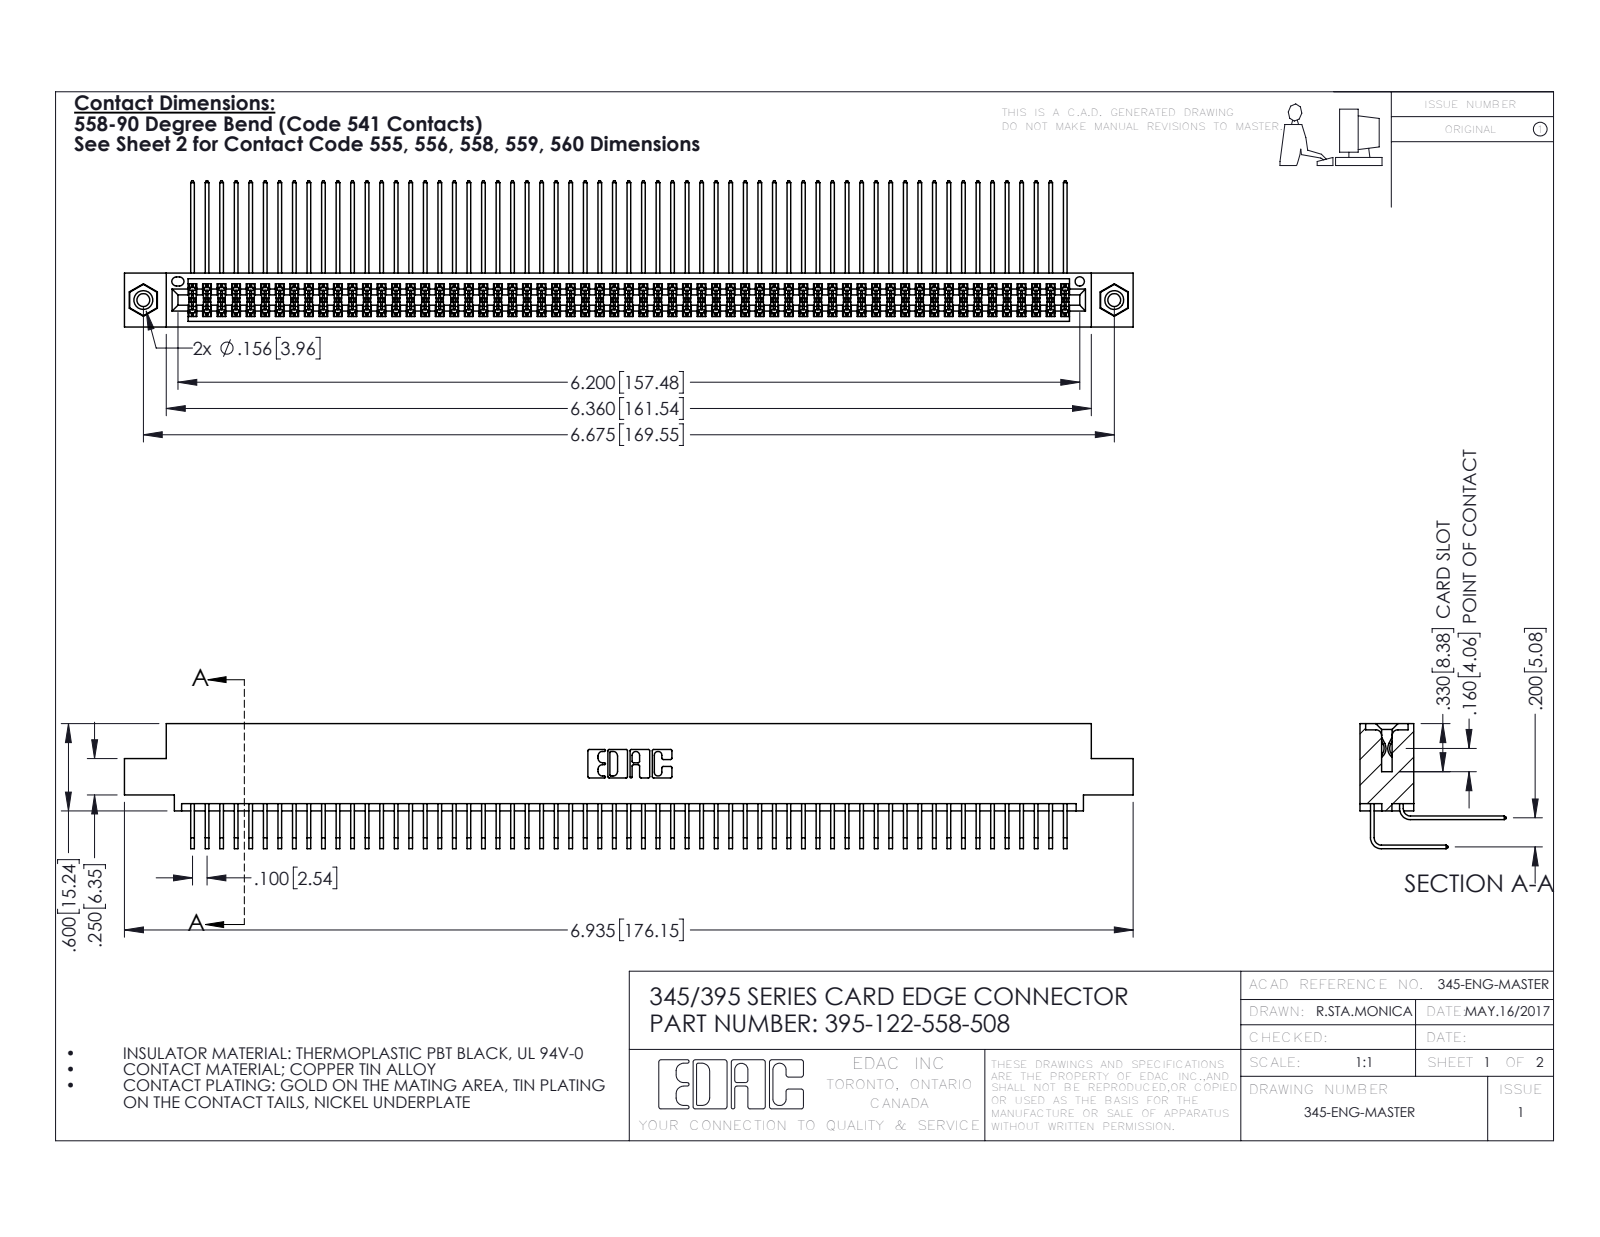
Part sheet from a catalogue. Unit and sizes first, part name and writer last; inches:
Units: inches
Overall size (bounding box): 6.935 × 1.005 × 0.859
Round holes (diameter × count): ⌀0.089 ×2, ⌀0.125 ×2, ⌀0.156 ×2, ⌀0.064 ×1
Round bosses / shafts (diameter × count): ⌀0.155 ×2
Partial cylindrical surfaces — rounded edges, fillets, slot ends (radius × count): R0.006 ×184, R0.01 ×22, R0.007 ×6, R0.031 ×6, R0.026 ×3, R0.014 ×2, R0.019 ×2, R0.022 ×2
Main face-to-face distances: 0.072, 0.298, 0.2, 0.37, 0.098, 0.272, 0.025, 0.225, 0.025, 0.175
Hole centre spacings: 0.27, 6.439, 6.675
Volume: 1.093 in³ · Surface area: 46.9 in²
Bodies: 125 solids, 6534 faces (4386 planar, 2132 cylindrical, 16 other)
Part name (STEP PRODUCT): 345-292-001_558 Tail - 2; 345-292-001_558 559 Tail - 1; 345-250-001_345-250-003-102; 395-122-558-508 (+1 more)
STEP written by: SolidWorks 2016 (CONFIG_CONTROL_DESIGN)
